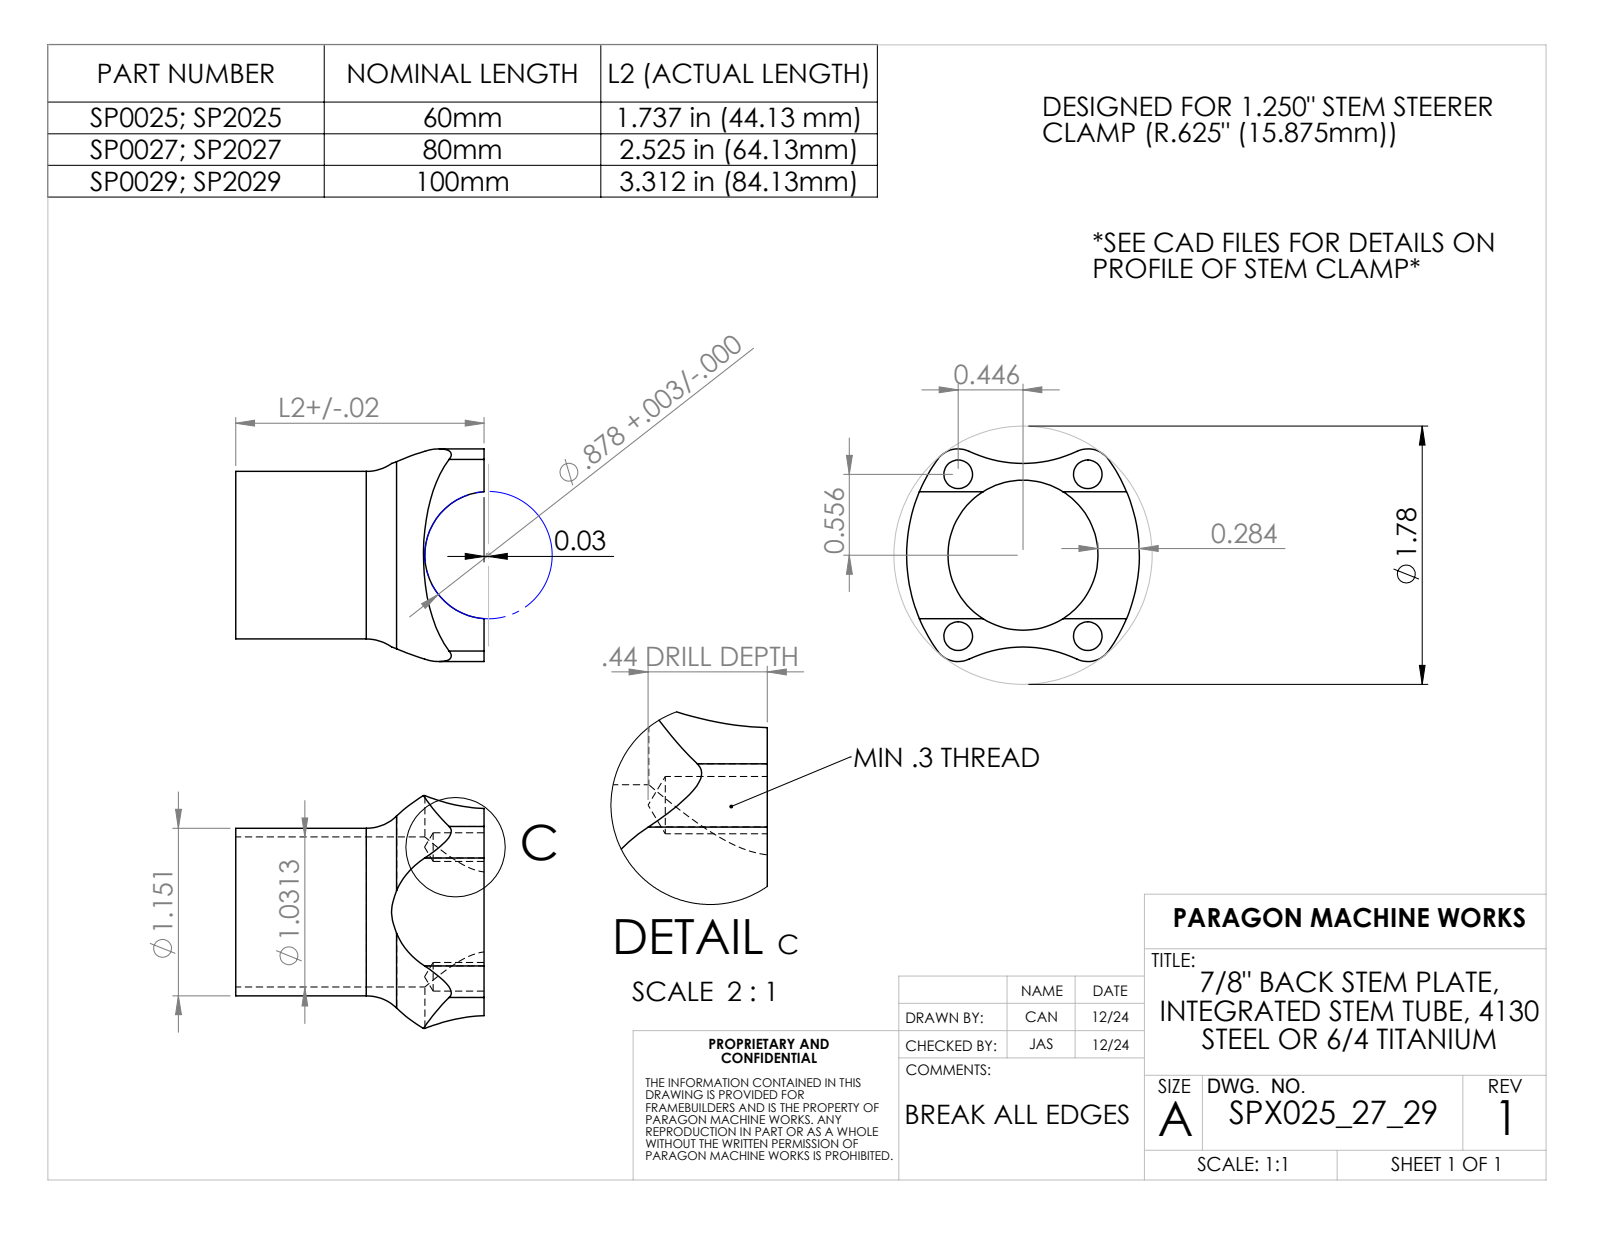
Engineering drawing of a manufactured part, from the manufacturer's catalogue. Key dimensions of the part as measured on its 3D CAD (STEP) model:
Part name (STEP PRODUCT): SP0025; SP4025_V2
STEP written by: SolidWorks 2023 (AUTOMOTIVE_DESIGN)
Units: millimetres
Bodies: 2 solids, 87 faces (9 planar, 62 cylindrical, 16 other)
Overall size (bounding box): 60.32 × 40.64 × 37.13
Volume: 19 527 mm³ · Surface area: 14 209 mm²
Round holes (diameter × count): ⌀5 ×4, ⌀5 ×4, ⌀22.22 ×1, ⌀26.19 ×1
Round bosses / shafts (diameter × count): ⌀29.24 ×1
Partial cylindrical surfaces — rounded edges, fillets, slot ends (radius × count): R0.51 ×4, R1.27 ×4, R4.45 ×4, R22.04 ×2, R28.6 ×2, R27.26 ×1
Main face-to-face distances: 0.77, 9.66, 8.89, 43.36, 44.13, 53.02
Hole centre spacings: 18.1, 22.63, 28.25, 36.2, 18.09, 18.11
